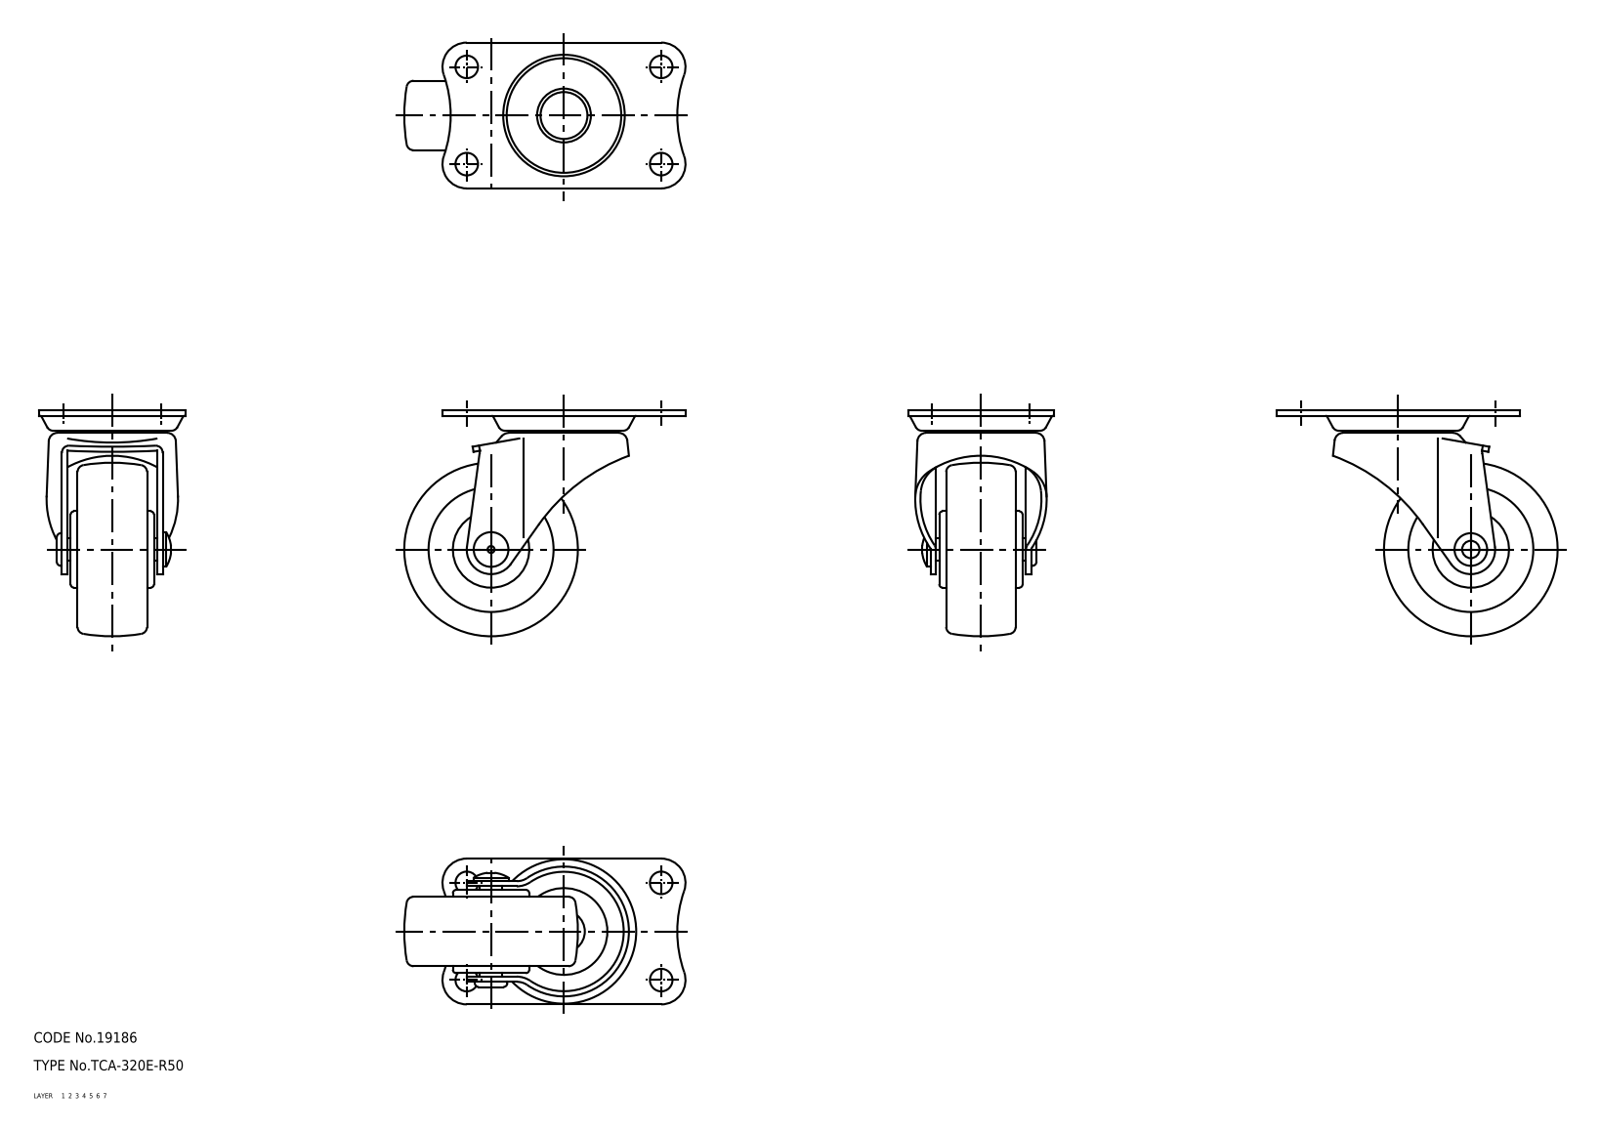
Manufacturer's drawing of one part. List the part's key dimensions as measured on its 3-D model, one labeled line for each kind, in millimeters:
Part name (STEP PRODUCT): wheel; mounting plate; main shaft; axle (+1 more)
STEP written by: CADfix (AUTOMOTIVE_DESIGN)
Units: millimetres
Bodies: 5 solids, 216 faces (0 planar, 0 cylindrical, 216 other)
Overall size (bounding box): 81 × 65 × 42
Volume: 51 755 mm³ · Surface area: 23 928 mm²
